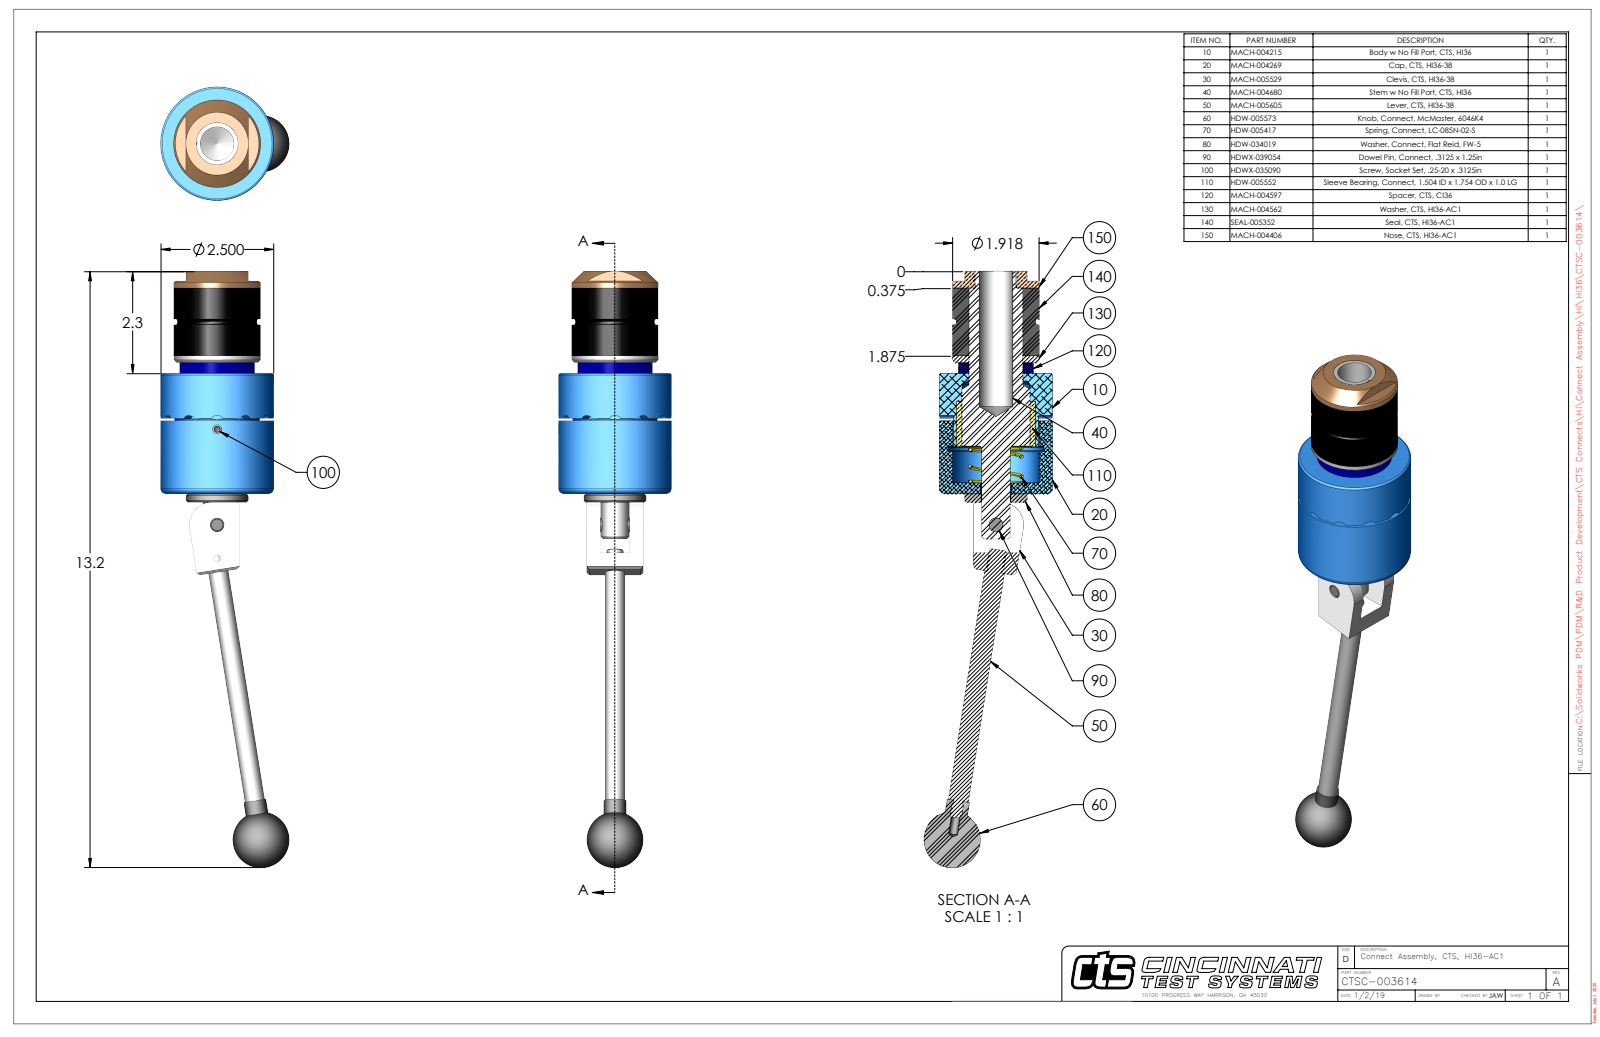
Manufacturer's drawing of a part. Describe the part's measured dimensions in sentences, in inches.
The part is named "CTSC-003614". Its 3-D file was written by "SolidWorks 2023 (AUTOMOTIVE_DESIGN)". It is 10 solids with 271 faces: 97 planar, 107 cylindrical and 67 other. Overall it measures 13.215 by 2.843 by 2.5 inches. Its volume is 21.23 cubic inches and its surface area 118.3 square inches. Round holes: 2 of diameter 0.201, 1 of diameter 0.15, 1 of diameter 0.311, 1 of diameter 0.313, 1 of diameter 0.314, 1 of diameter 0.656, 1 of diameter 0.696, 1 of diameter 0.75, 1 of diameter 0.922, 1 of diameter 1.188, 1 of diameter 1.19, 1 of diameter 1.195. Round bosses or shafts: 1 of diameter 2.5, 1 of diameter 1.918, 1 of diameter 1.875, 1 of diameter 1.656, 1 of diameter 1.38, 1 of diameter 1.186, 1 of diameter 1, 1 of diameter 0.904. Partial cylindrical surfaces (rounded edges, fillets, slot ends): 12 of radius 0.12, 2 of radius 0.029, 1 of radius 0.5, 1 of radius 1.179. The main face-to-face distances are 2.668, 4.555, 1.887, 3.055, 0.387, 1.5, 2.905, 0.237, 0.15, 1.65. The hole center spacings are 0.74, 2.118, 2.858.
